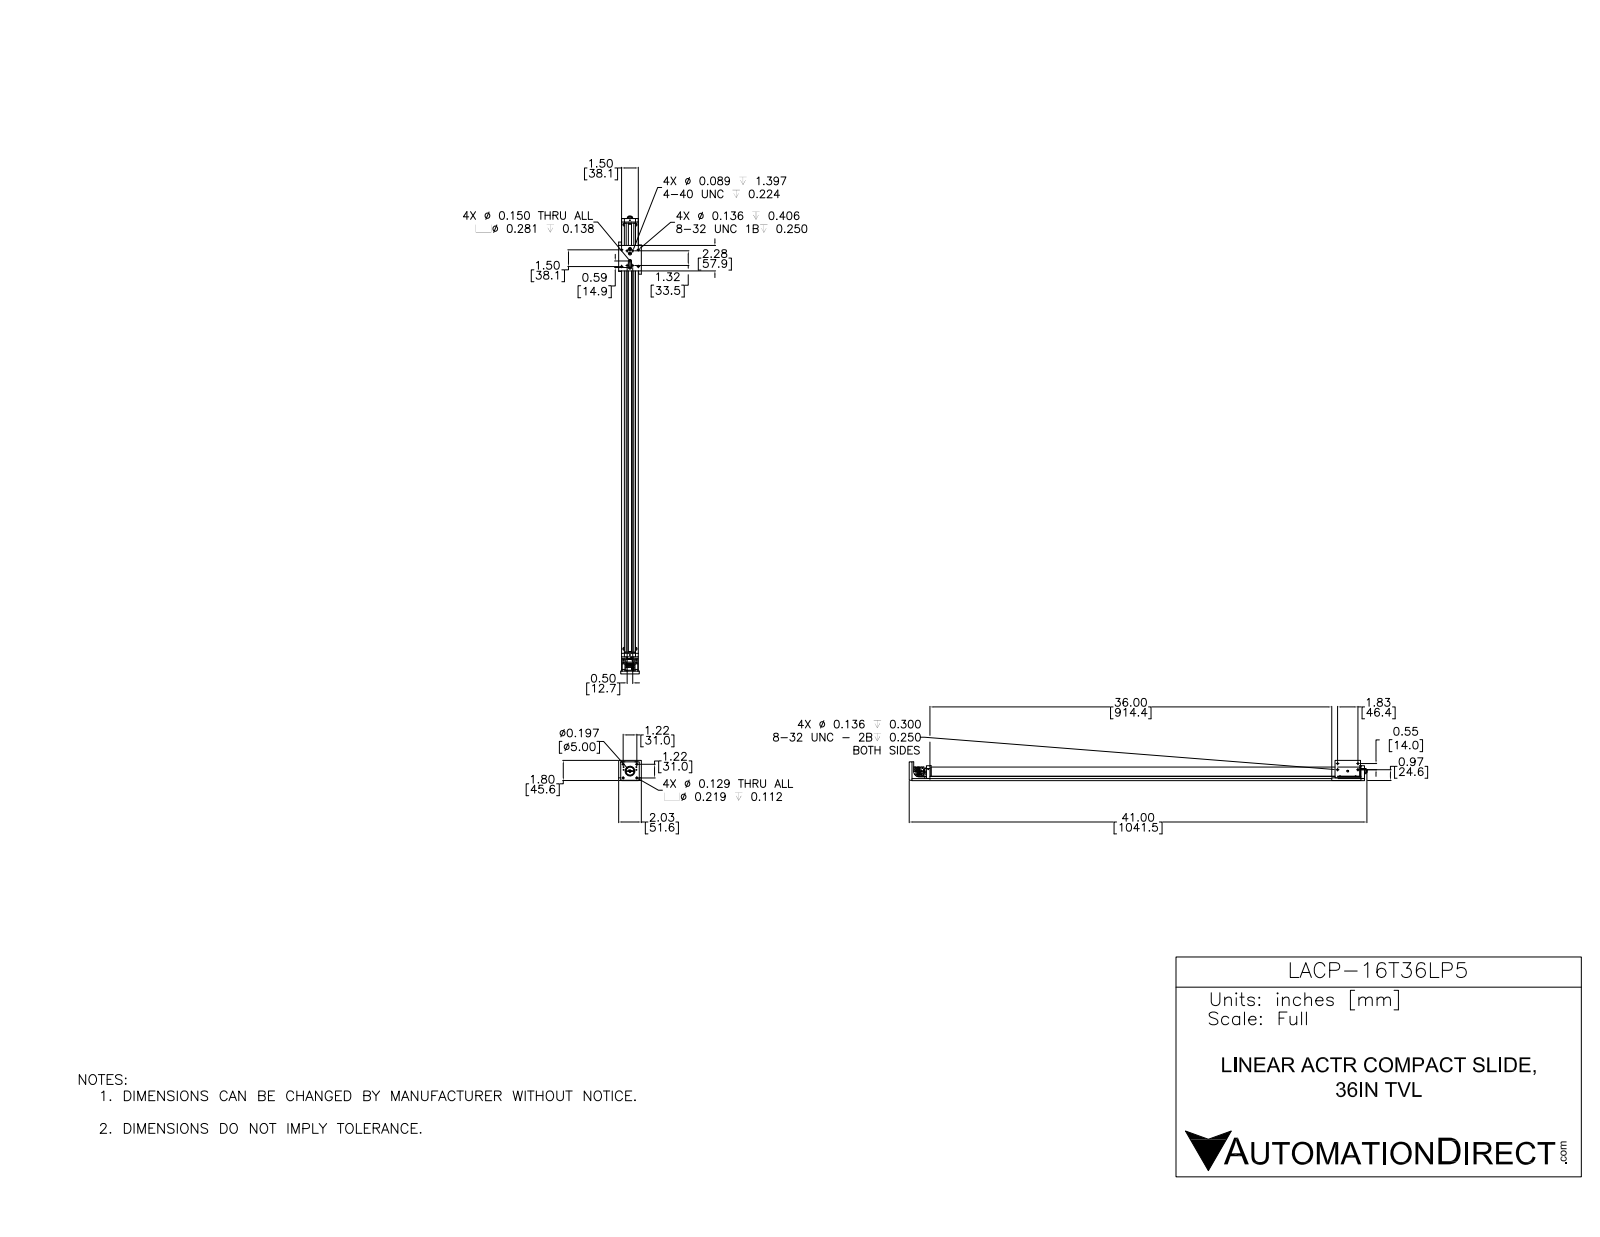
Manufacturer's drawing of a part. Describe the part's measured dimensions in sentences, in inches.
The part is named "LACP-16T36LP5; LACP-16TXXLP5-CAR; LACP-16T36LP5-RAIL". Its 3-D file was written by "SolidWorks 2016 (AUTOMOTIVE_DESIGN)". It is 25 solids with 947 faces: 289 planar, 562 cylindrical and 96 other. Overall it measures 40.995 by 2.03 by 1.812 inches. Its volume is 42.27 cubic inches and its surface area 463.6 square inches. Round holes: 22 of diameter 0.281, 20 of diameter 0.17, 16 of diameter 0.089, 12 of diameter 0.15, 10 of diameter 0.138, 10 of diameter 0.28, 8 of diameter 0.136, 4 of diameter 0.07, 4 of diameter 0.129, 4 of diameter 0.129, 4 of diameter 0.219, 3 of diameter 0.197. Round bosses or shafts: 3 of diameter 0.157, 2 of diameter 0.15, 1 of diameter 1, 1 of diameter 0.748, 1 of diameter 0.71, 1 of diameter 0.673, 1 of diameter 0.67, 1 of diameter 0.59. Partial cylindrical surfaces (rounded edges, fillets, slot ends): 4 of radius 0.047, 4 of radius 0.062, 4 of radius 0.094, 3 of radius 0.125, 2 of radius 0.05, 2 of radius 0.075, 2 of radius 0.141, 2 of radius 0.25. The main face-to-face distances are 0.187, 1.219, 1.031, 0.265, 1.765, 1.5, 0.875, 1.155, 0.61, 0.89. The hole center spacings are 4.031, 8, 4, 4.123, 8.016, 8.062, 12.01, 12.
